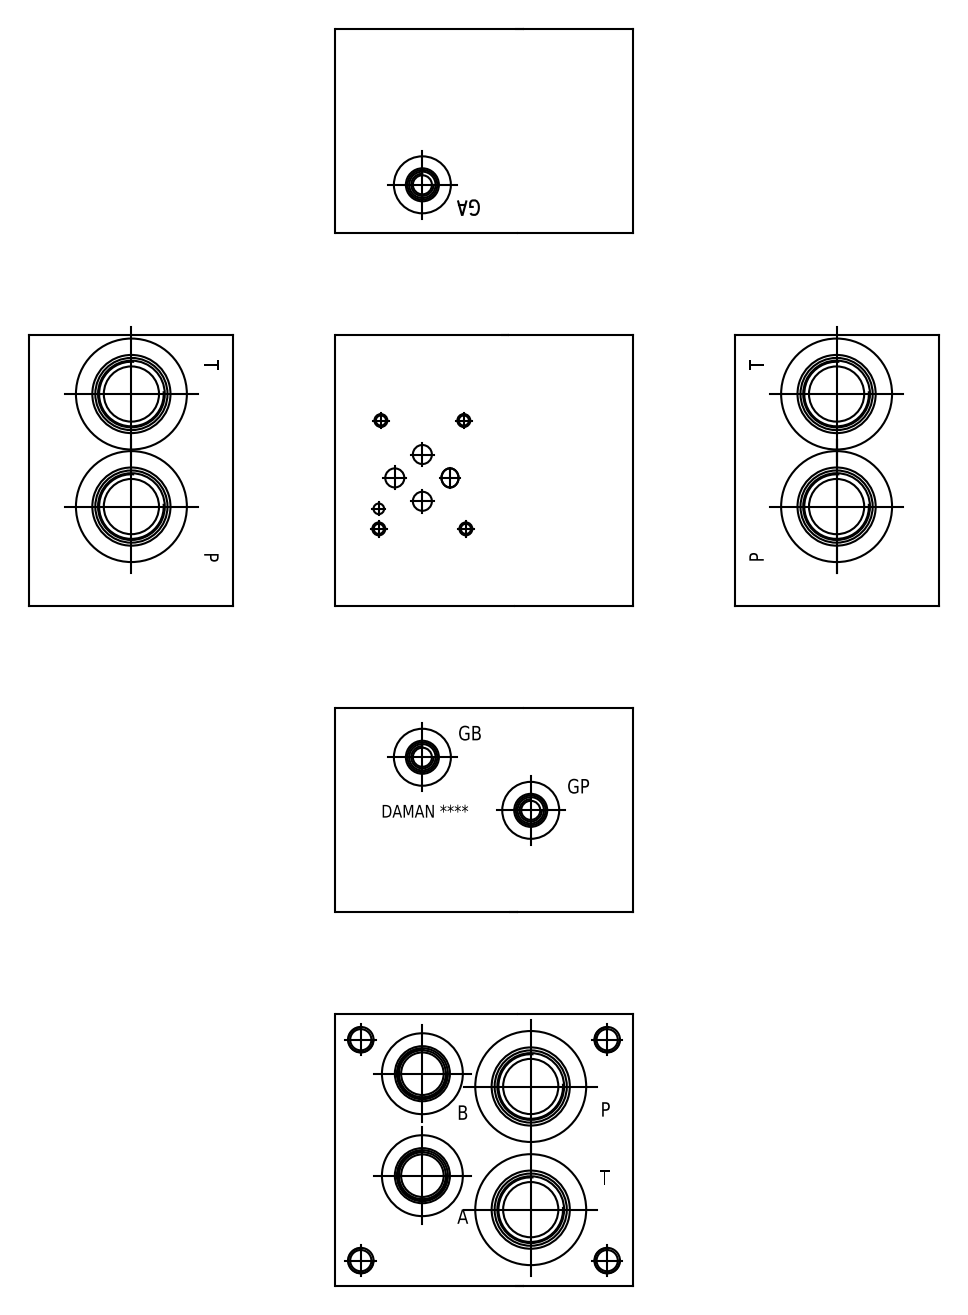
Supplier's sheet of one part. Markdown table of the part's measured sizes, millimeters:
| quantity | value |
| --- | --- |
| part name | Part_DD03PB012S_3D |
| STEP written by | Autodesk Inventor 2019 (AUTOMOTIVE_DESIGN) |
| units | millimeters |
| bodies | 1 solid, 737 faces (400 planar, 71 cylindrical, 266 other) |
| overall size | 111.12 × 101.6 × 76.2 |
| volume | 731 722 mm³ |
| surface area | 77 430 mm² |
| round holes (diameter × count) | 7.14 × 5, 9.53 × 5, 3.78 × 4, 4.83 × 4, 7.92 × 4, 24.92 × 4, 26.99 × 4, 27.43 × 4, 42.04 × 4, 9.88 × 3, 11.13 × 3, 21.29 × 3 |
| main face-to-face distances | 101.6, 76.2, 111.12, 0.79, 75.41, 110.33, 110.34, 109.55, 0.78, 100.81 |
| hole center spacings | 13.52, 13.54, 19.95, 22.05, 32.71, 33.55, 40.5, 50.28 |
